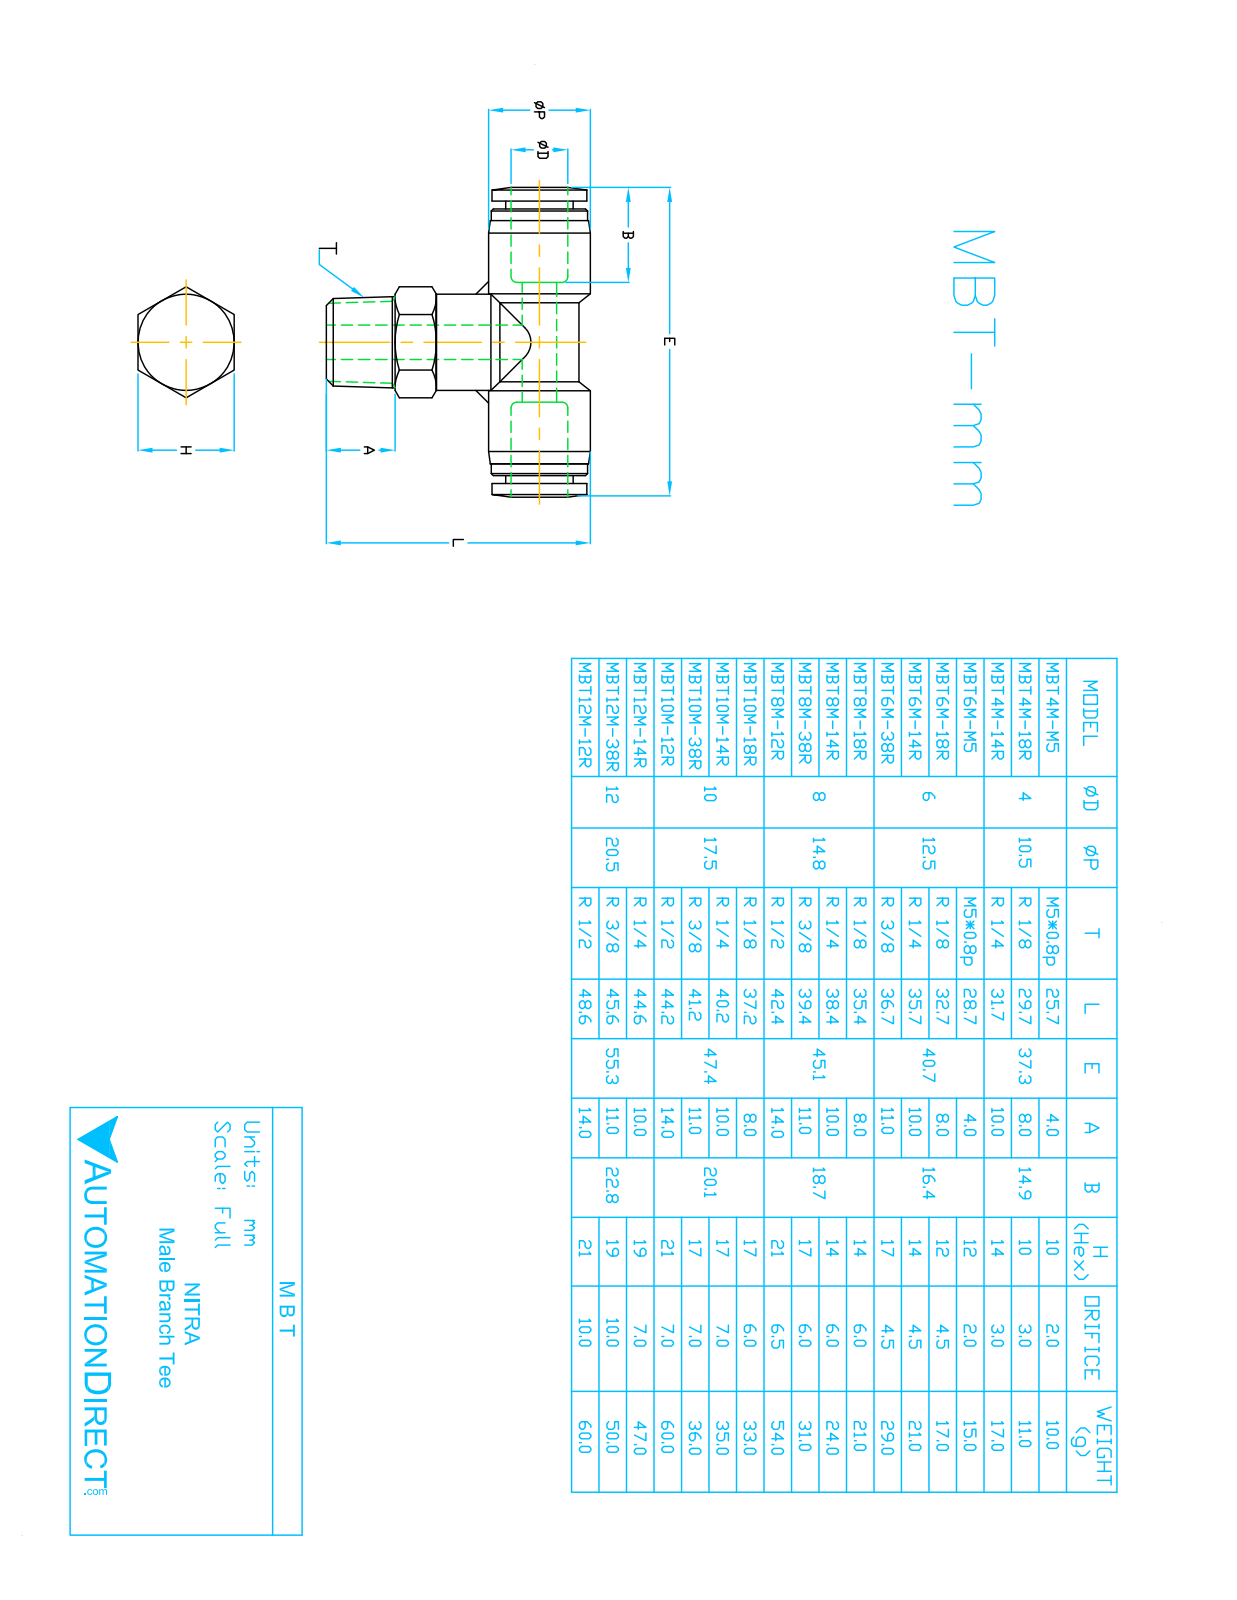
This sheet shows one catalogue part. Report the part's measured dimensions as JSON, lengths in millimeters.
{"part_name": "MBT6M-38R", "step_written_by": "SolidWorks 2015 (AUTOMOTIVE_DESIGN)", "units": "millimeters", "bodies": {"solids": 1, "faces": 96, "planar": 25, "cylindrical": 31, "other": 40}, "overall_size": [40.6, 36.8, 17], "volume_mm3": 7540, "surface_area_mm2": 4500, "round_holes": [[4, 2], [6.3, 1]], "round_bosses_or_shafts": [[12, 2], [12.5, 1], [11.8, 1], [7.7, 1]], "partial_cylinders_radius": [[4.7, 2]], "face_to_face_distances": [17, 1.1, 35.8, 37, 34.7, 14.6, 22.4, 13.5, 21.3, 7.8]}
